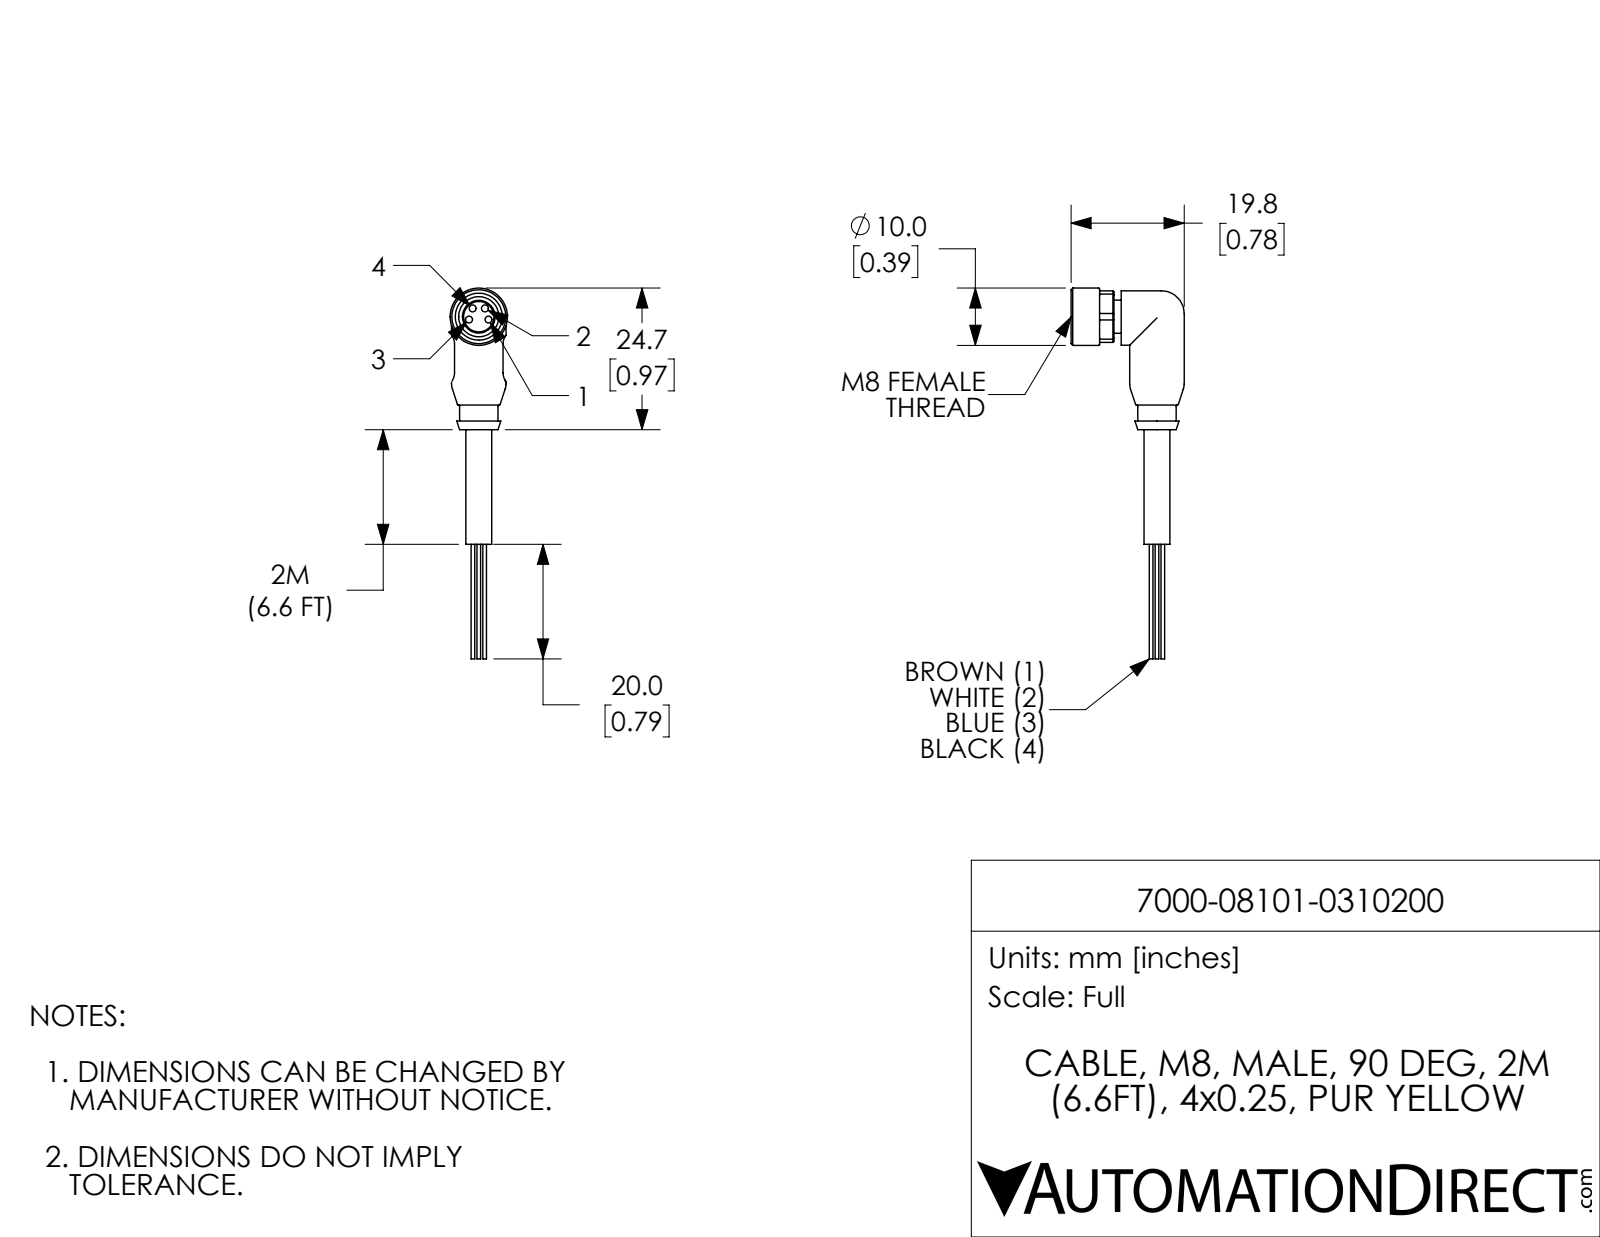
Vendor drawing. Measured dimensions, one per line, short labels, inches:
name: 7000-08101-0310200
written by: SolidWorks 2021 (CONFIG_CONTROL_DESIGN)
unit: in
bodies: 5 solids, 117 faces (41 planar, 47 cylindrical, 29 other)
size: 2.548 × 0.778 × 0.394
volume: 0.147 in³; area: 2.976 in²
holes: 4× ⌀0.047, 1× ⌀0.276
bosses: 3× ⌀0.025, 2× ⌀0.374, 1× ⌀0.394, 1× ⌀0.264, 1× ⌀0.228, 1× ⌀0.224, 1× ⌀0.177, 1× ⌀0.025
rounds: 4× R0.008, 4× R0.098, 1× R0.193
face distances: 0.049, 0.354, 0.059, 0.335, 0.028, 0.787, 0.268, 0.317, 0.295, 0.344
hole spacings: 0.07, 0.071, 0.081, 0.133, 0.084, 0.134
